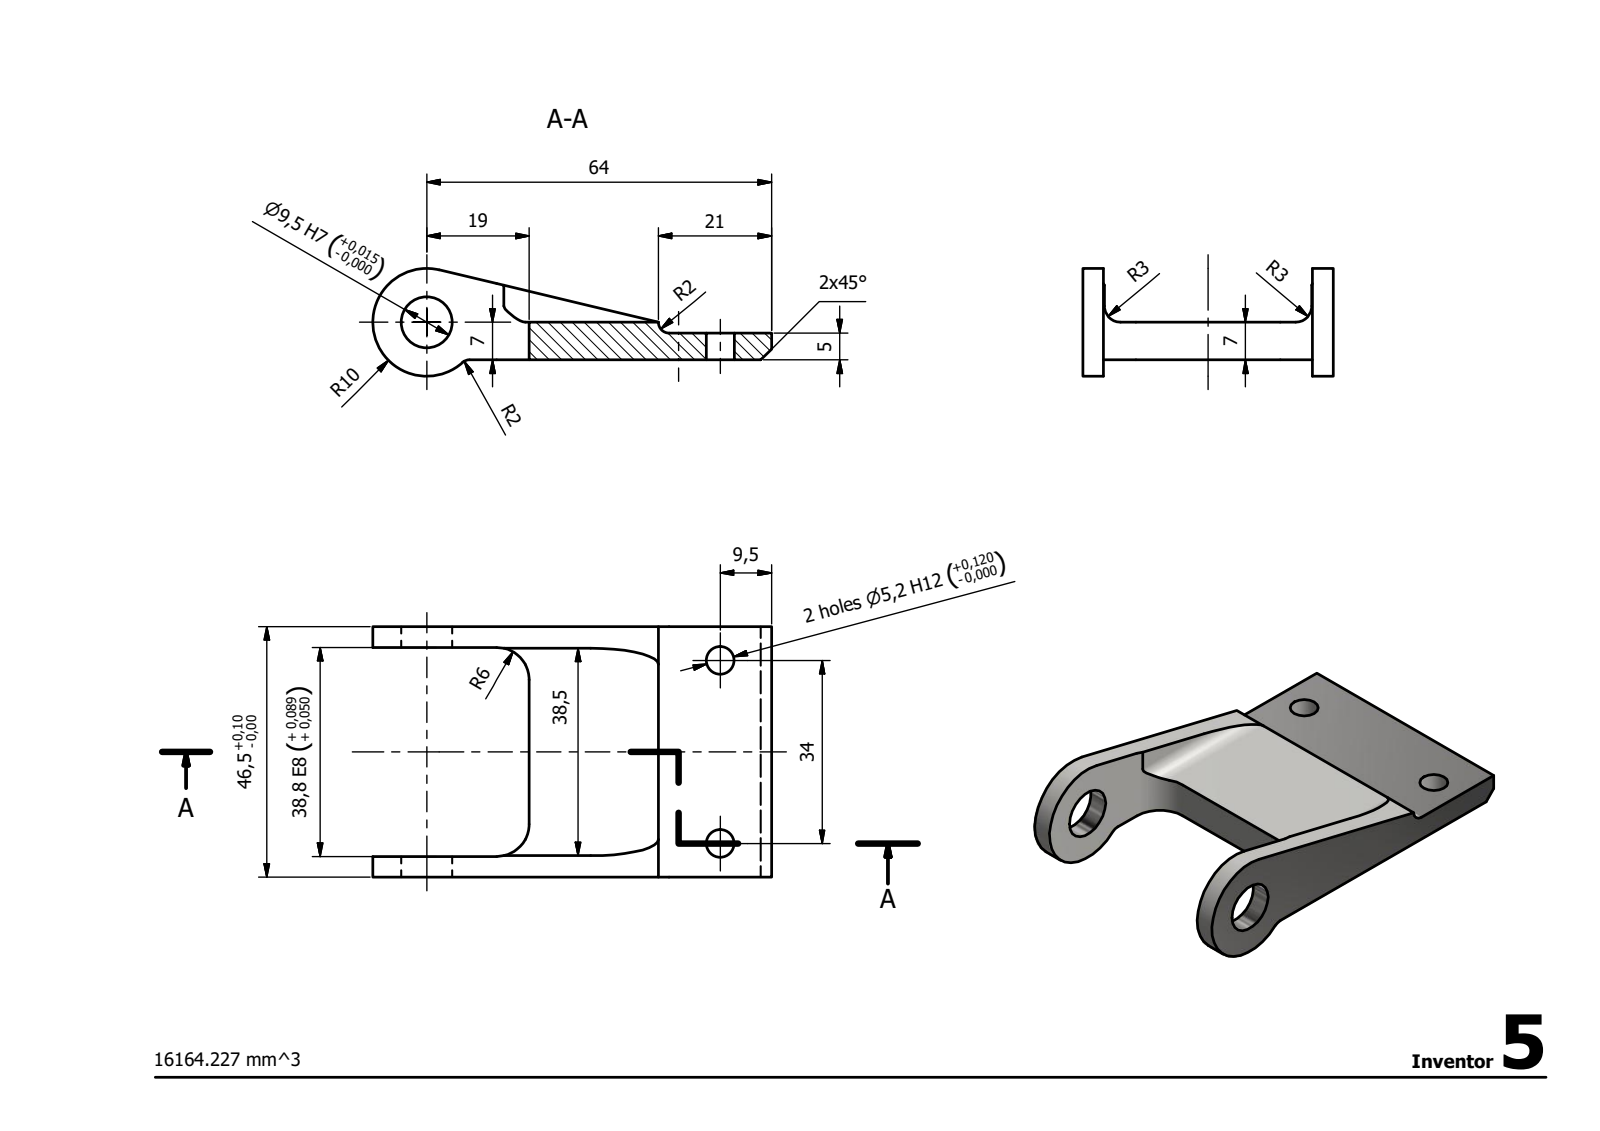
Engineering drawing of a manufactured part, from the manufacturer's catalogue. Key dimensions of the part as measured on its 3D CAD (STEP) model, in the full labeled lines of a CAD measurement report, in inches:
STEP written by: Autodesk Inventor 2014 (AUTOMOTIVE_DESIGN)
Units: inches
Bodies: 1 solid, 27 faces (14 planar, 13 cylindrical, 0 other)
Overall size (bounding box): 2.913 × 1.831 × 0.787
Volume: 0.986 in³ · Surface area: 12.16 in²
Round holes (diameter × count): ⌀0.205 ×2, ⌀0.374 ×1
Partial cylindrical surfaces — rounded edges, fillets, slot ends (radius × count): R0.079 ×2, R0.118 ×2, R0.236 ×2, R0.394 ×1
Main face-to-face distances: 0.197, 0.276, 0.079, 1.831, 0.152, 1.679, 1.528, 1.772, 0.157, 1.673
Hole centre spacings: 1.339
